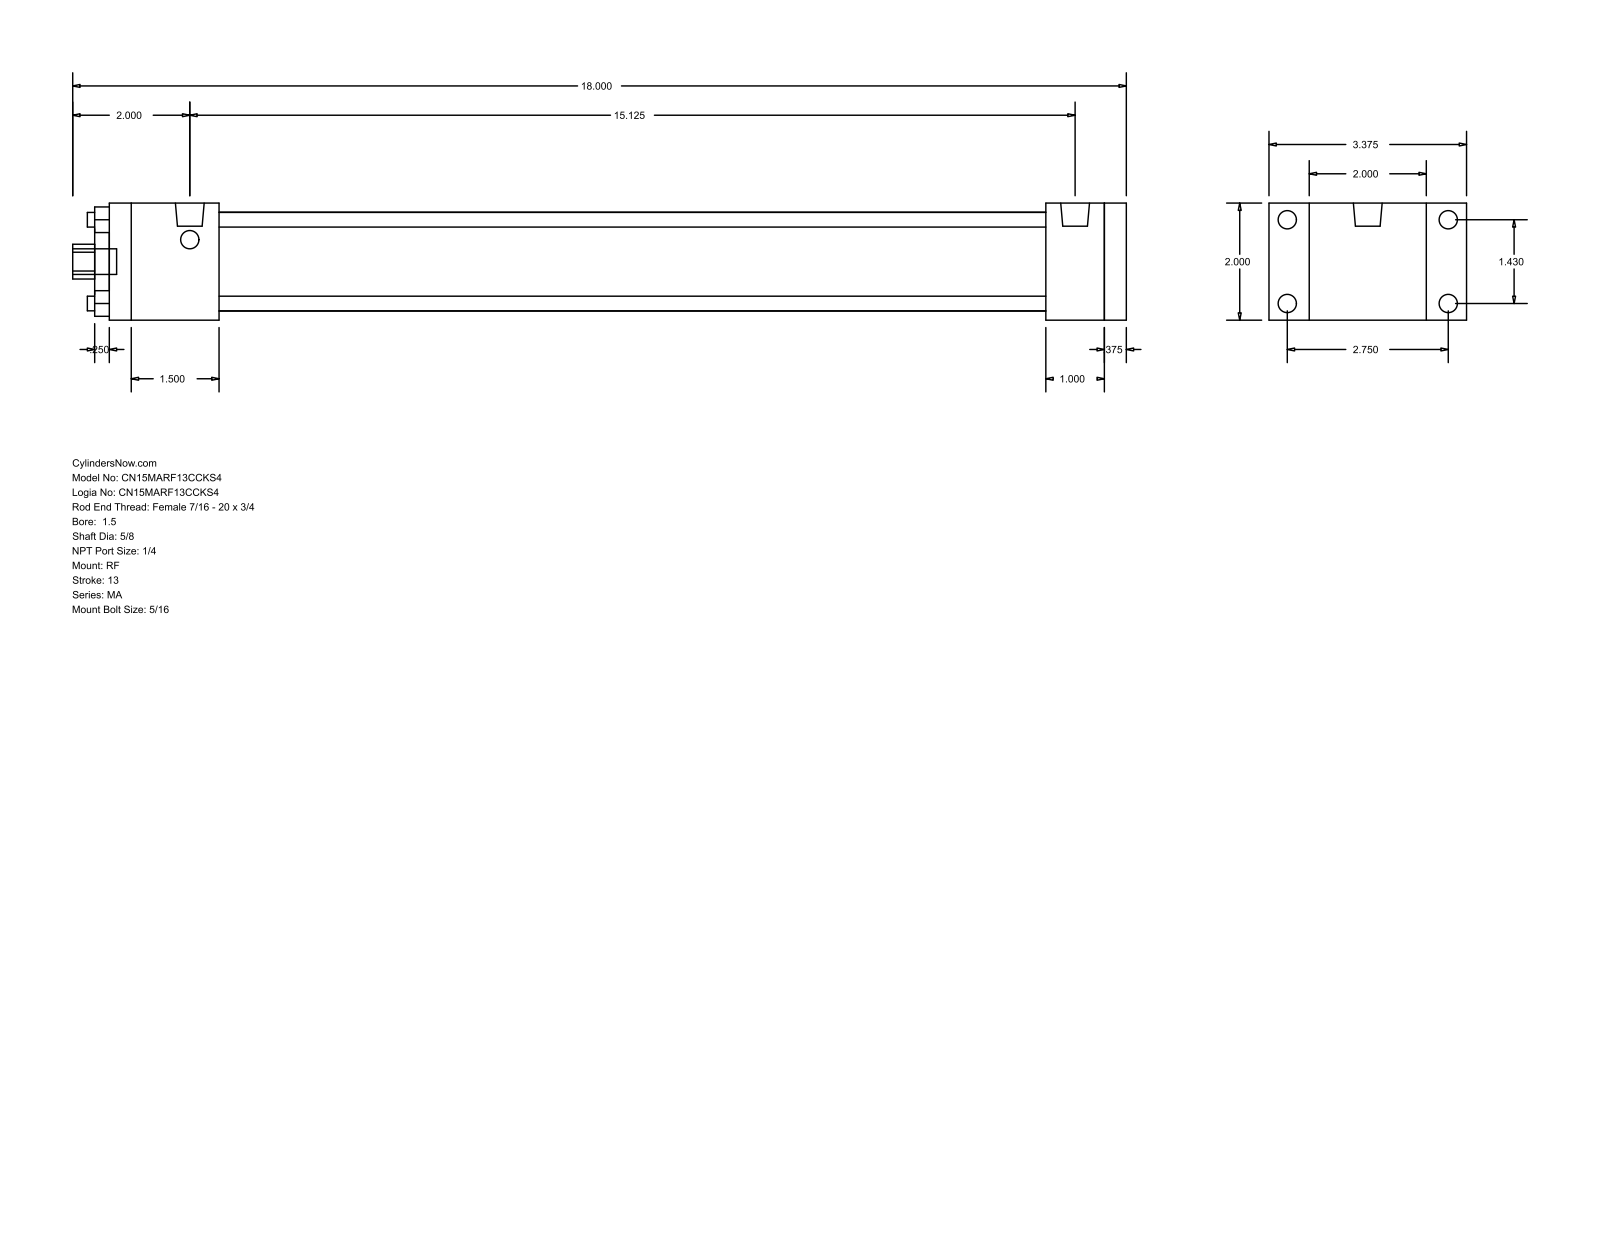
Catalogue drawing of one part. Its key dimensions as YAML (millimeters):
part_name: "MA_RF__0150_0.625"
step_written_by: "GSSL Pune (CONFIG_CONTROL_DESIGN)"
units: millimeters
bodies: {solids: 0, faces: 92, planar: 64, cylindrical: 28, other: 0}
overall_size: [457.2, 85.72, 50.8]
round_holes:
  - {diameter: 6.35, count: 4}
  - {diameter: 15.88, count: 1}
  - {diameter: 28.57, count: 1}
  - {diameter: 42.93, count: 1}
round_bosses_or_shafts:
  - {diameter: 7.94, count: 8}
  - {diameter: 12.49, count: 2}
  - {diameter: 11.11, count: 1}
partial_cylinders:
  - {radius: 7.54, count: 1}
face_to_face_distances: [50.8, 9.52, 431.8, 441.32, 406.39, 25.41, 34.93, 47.62, 358.77, 384.18]
hole_center_spacings: [25.68, 36.32, 51.36]
